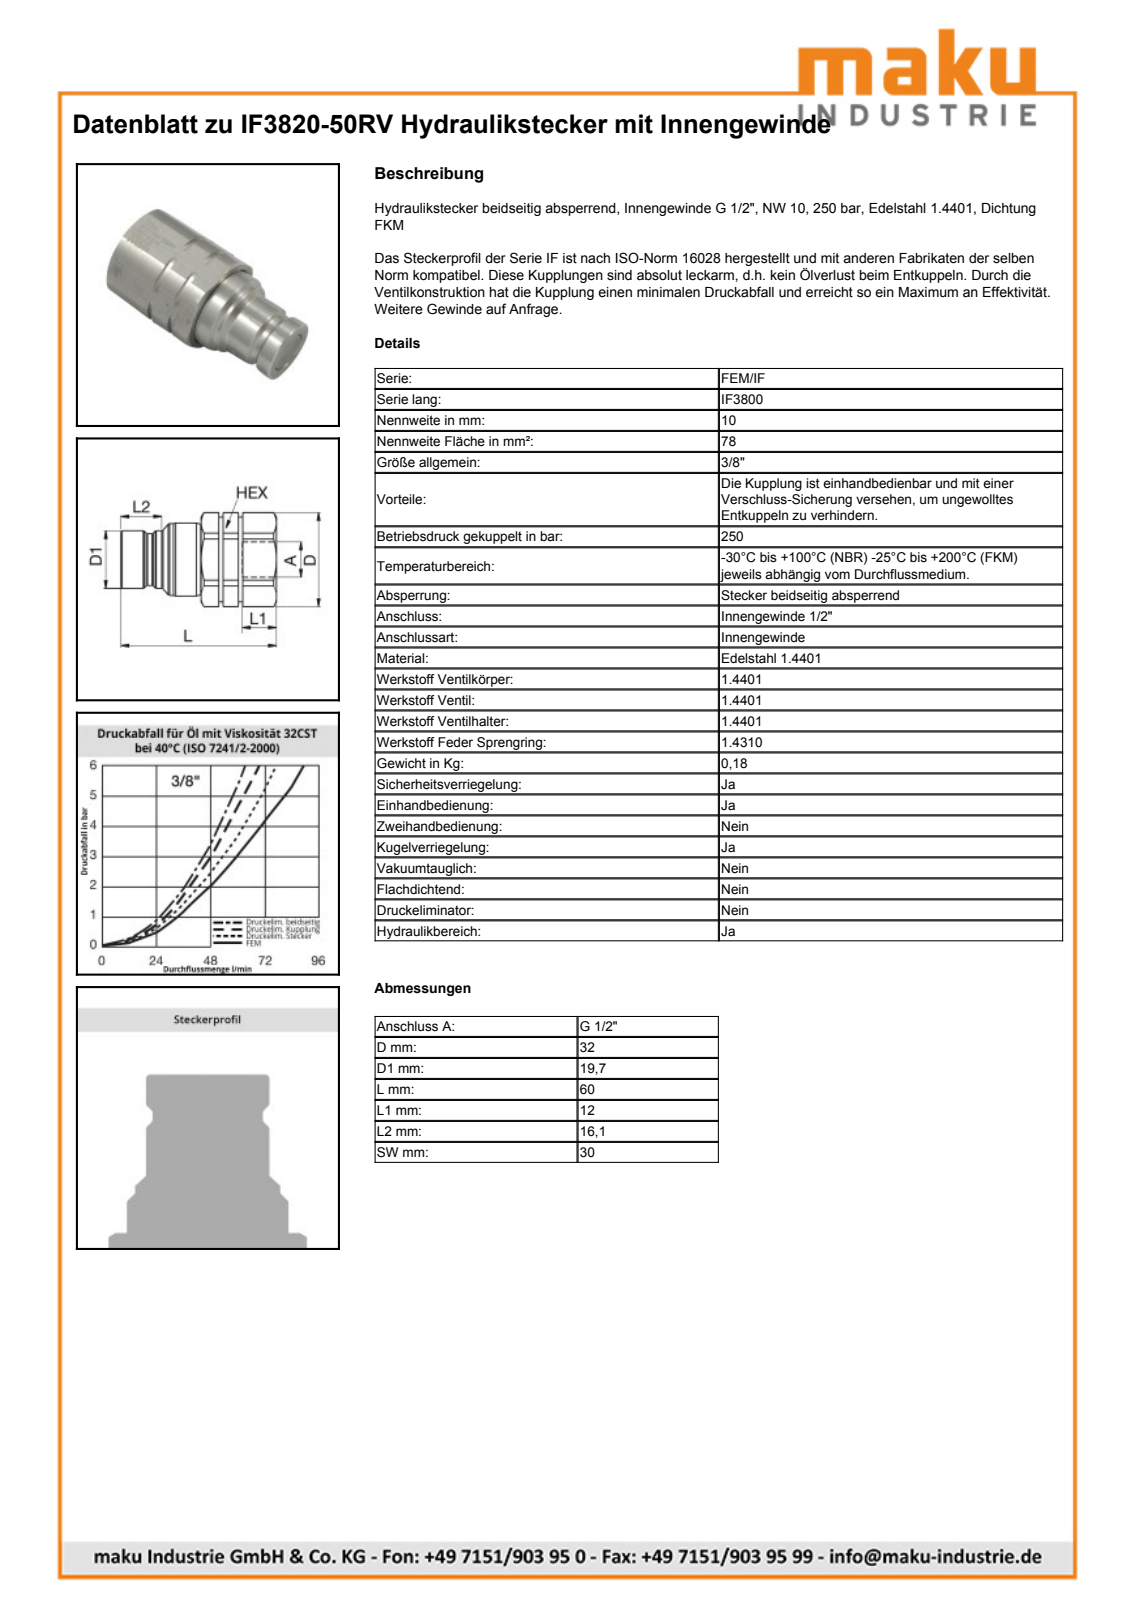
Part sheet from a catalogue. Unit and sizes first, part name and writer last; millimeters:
Units: millimetres
Overall size (bounding box): 60 × 32 × 30
Round holes (diameter × count): ⌀14.5 ×1, ⌀18.63 ×1, ⌀26.2 ×1
Round bosses / shafts (diameter × count): ⌀26 ×1, ⌀23.3 ×1, ⌀19.75 ×1, ⌀17.6 ×1
Partial cylindrical surfaces — rounded edges, fillets, slot ends (radius × count): R15.15 ×1, R16 ×1
Main face-to-face distances: 30, 60, 26, 34, 40.98, 19.02, 14.98, 1.65, 8.15, 32.35
Volume: 29 996 mm³ · Surface area: 7 886 mm²
Bodies: 1 solid, 132 faces (36 planar, 46 cylindrical, 50 other)
Part name (STEP PRODUCT): IF3820-50RV
STEP written by: SolidWorks 2009 (AUTOMOTIVE_DESIGN)
